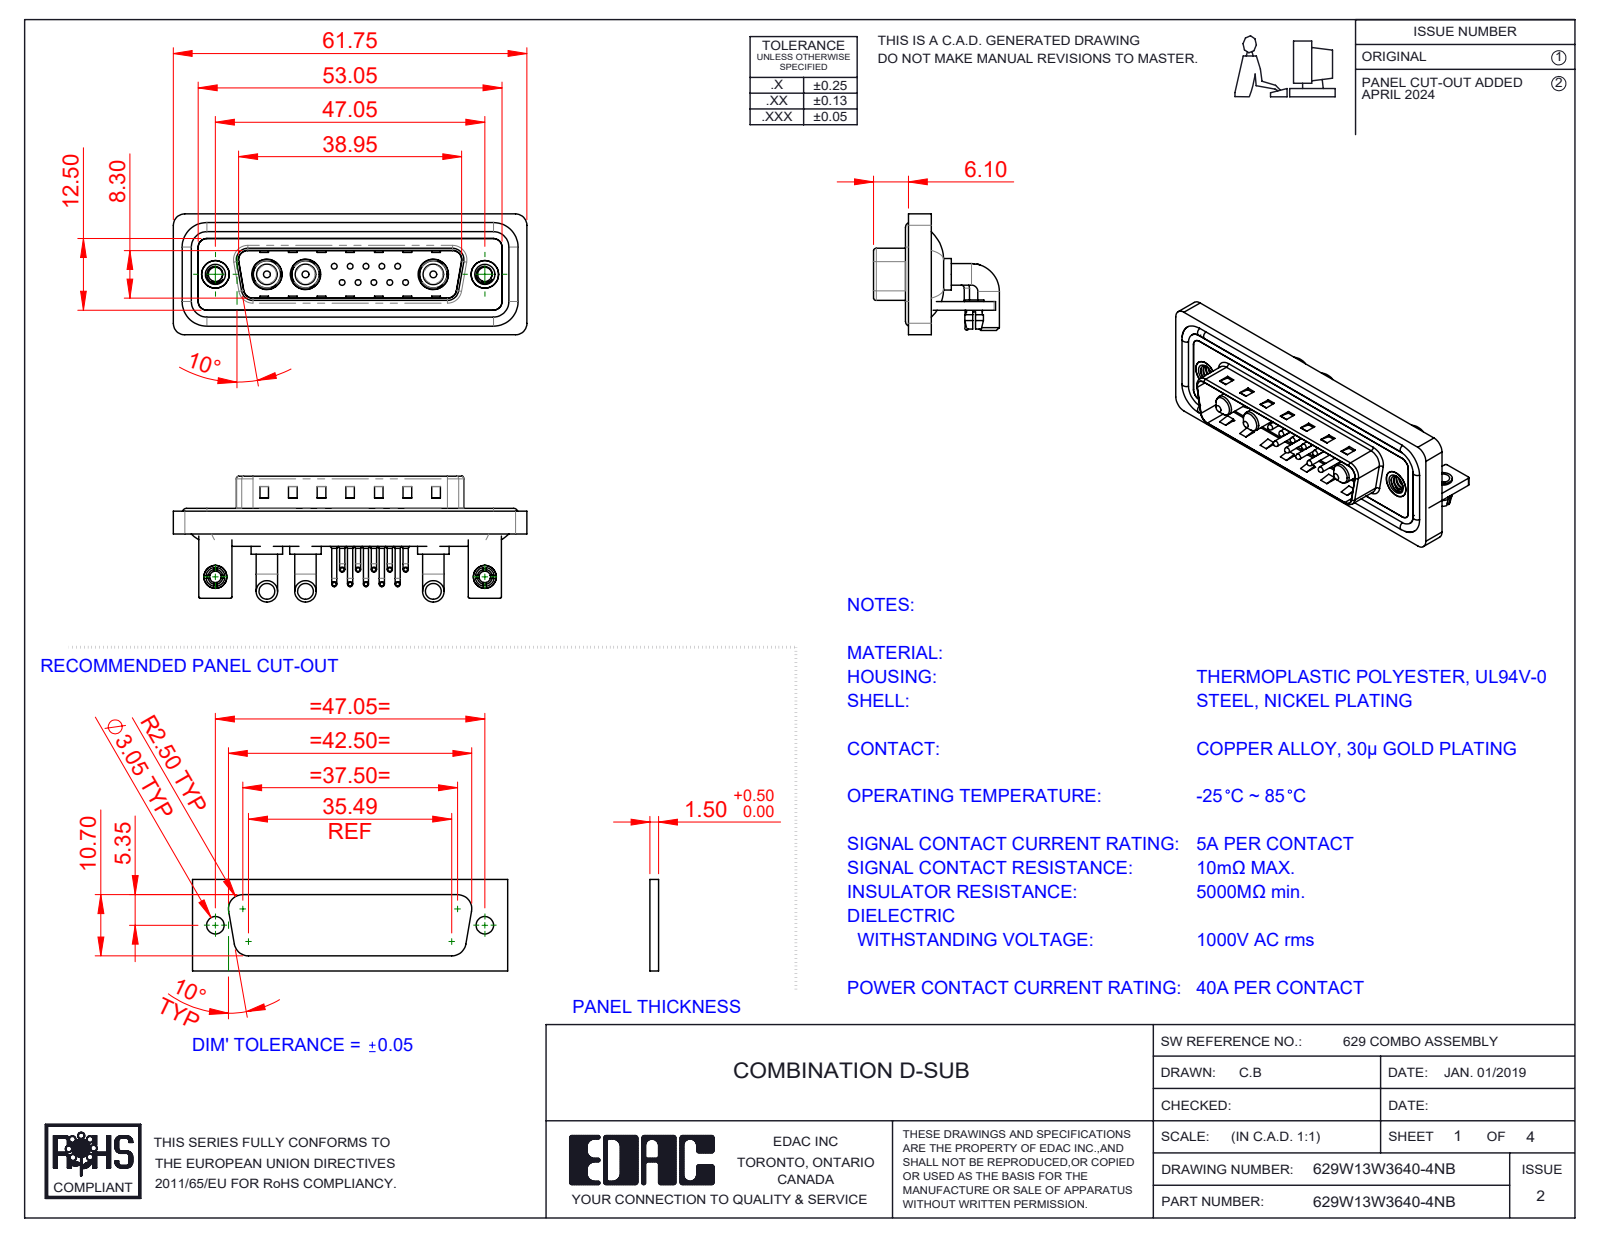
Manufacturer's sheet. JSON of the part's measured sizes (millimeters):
{"part_name": "629Combo Threaded Rivet_B; 629Combo Waterproof Housing_25 Contacts; 629Combo Shell Front_25 Contacts; 629W13W3640-4NB (+7 more)", "step_written_by": "SolidWorks 2023 (CONFIG_CONTROL_DESIGN)", "units": "millimeters", "bodies": {"solids": 27, "faces": 1842, "planar": 947, "cylindrical": 661, "other": 234}, "overall_size": [61.75, 21.98, 21.1], "volume_mm3": 8137, "surface_area_mm2": 13427, "round_holes": [[2, 12], [0.75, 10], [1.6, 10], [2.5, 4], [4.85, 3], [5.3, 3], [3.2, 2], [4, 2], [4.8, 2], [5, 2]], "round_bosses_or_shafts": [[0.9, 20], [1.5, 10], [1, 10], [0.65, 10], [3.75, 6], [1.6, 4], [5.5, 3], [5.2, 3]], "partial_cylinders_radius": [[2, 19], [1.5, 18], [0.25, 16], [1.01, 10], [0.5, 9], [1.6, 8], [0.6, 4], [0.65, 4]], "face_to_face_distances": [0.4, 0.8, 1.5, 2.9, 2.1, 1.1, 4.1, 1.6, 3.7, 4.5], "hole_center_spacings": [3.16, 2.77, 5.04, 5.54, 7.49, 5.03, 8.31, 10.11]}
